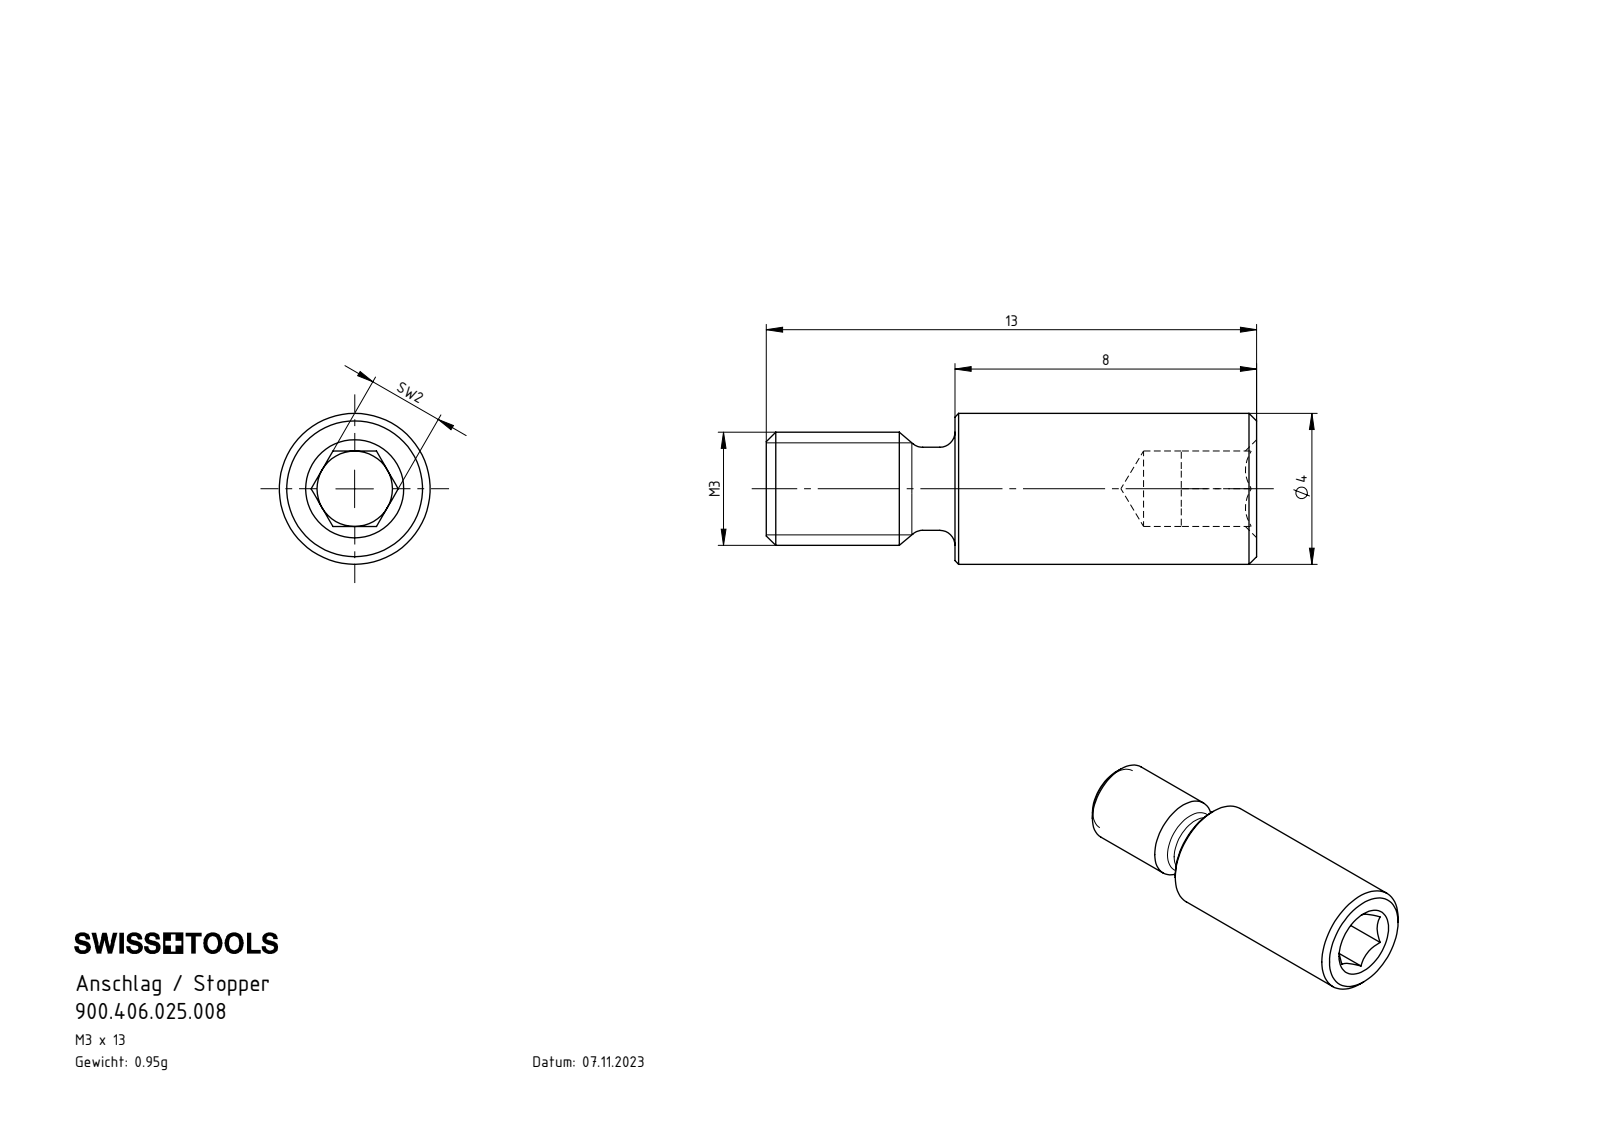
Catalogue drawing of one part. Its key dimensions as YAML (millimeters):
part_name: "900.406.025.008"
step_written_by: "SolidWorks 2022 (AUTOMOTIVE_DESIGN)"
units: millimeters
bodies: {solids: 1, faces: 39, planar: 15, cylindrical: 8, other: 16}
overall_size: [13, 4, 4]
volume: 121
surface_area: 189
round_holes:
  - {diameter: 2, count: 1}
round_bosses_or_shafts:
  - {diameter: 4, count: 1}
  - {diameter: 3, count: 1}
  - {diameter: 2.2, count: 1}
face_to_face_distances: [2, 13, 5, 8, 11, 6]
